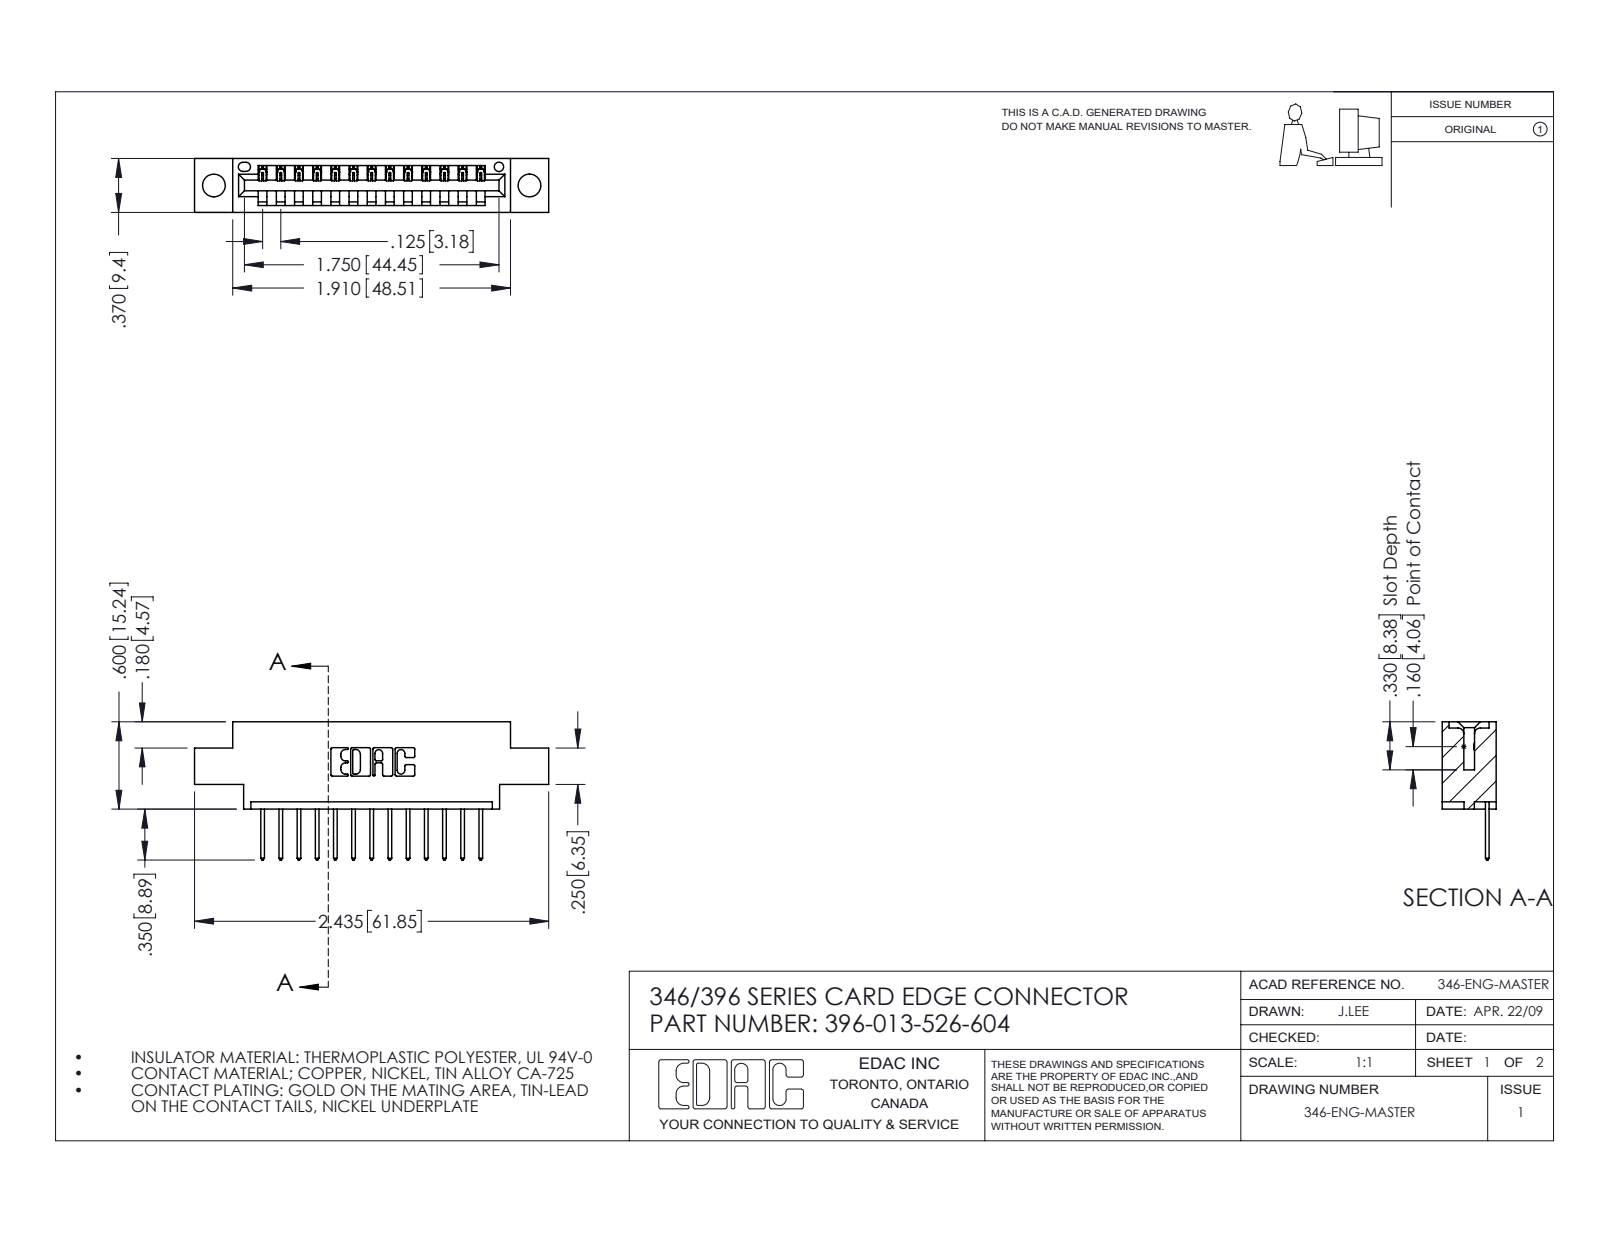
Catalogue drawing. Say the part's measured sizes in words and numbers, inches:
The part is named "345-292-001_345-293-126; 396-013-526-604; 346 Part_0.170 Offset - 0.156 Dia-TH". Its 3-D file was written by "SolidWorks 2016 (CONFIG_CONTROL_DESIGN)". It is 14 solids with 880 faces: 600 planar, 280 cylindrical and 0 other. Overall it measures 2.435 by 0.95 by 0.37 inches. Its volume is 0.334 cubic inches and its surface area 10.03 square inches. Round holes: 2 of diameter 0.156, 1 of diameter 0.064. Partial cylindrical surfaces (rounded edges, fillets, slot ends): 26 of radius 0.006, 26 of radius 0.01, 22 of radius 0.01, 6 of radius 0.007, 6 of radius 0.031, 3 of radius 0.026, 2 of radius 0.031, 2 of radius 0.04. The main face-to-face distances are 0.25, 0.37, 0.048, 0.322, 0.072, 0.298, 0.025, 0.148, 0.222, 0.1. The hole center spacings are 0.246, 1.964, 2.17.
